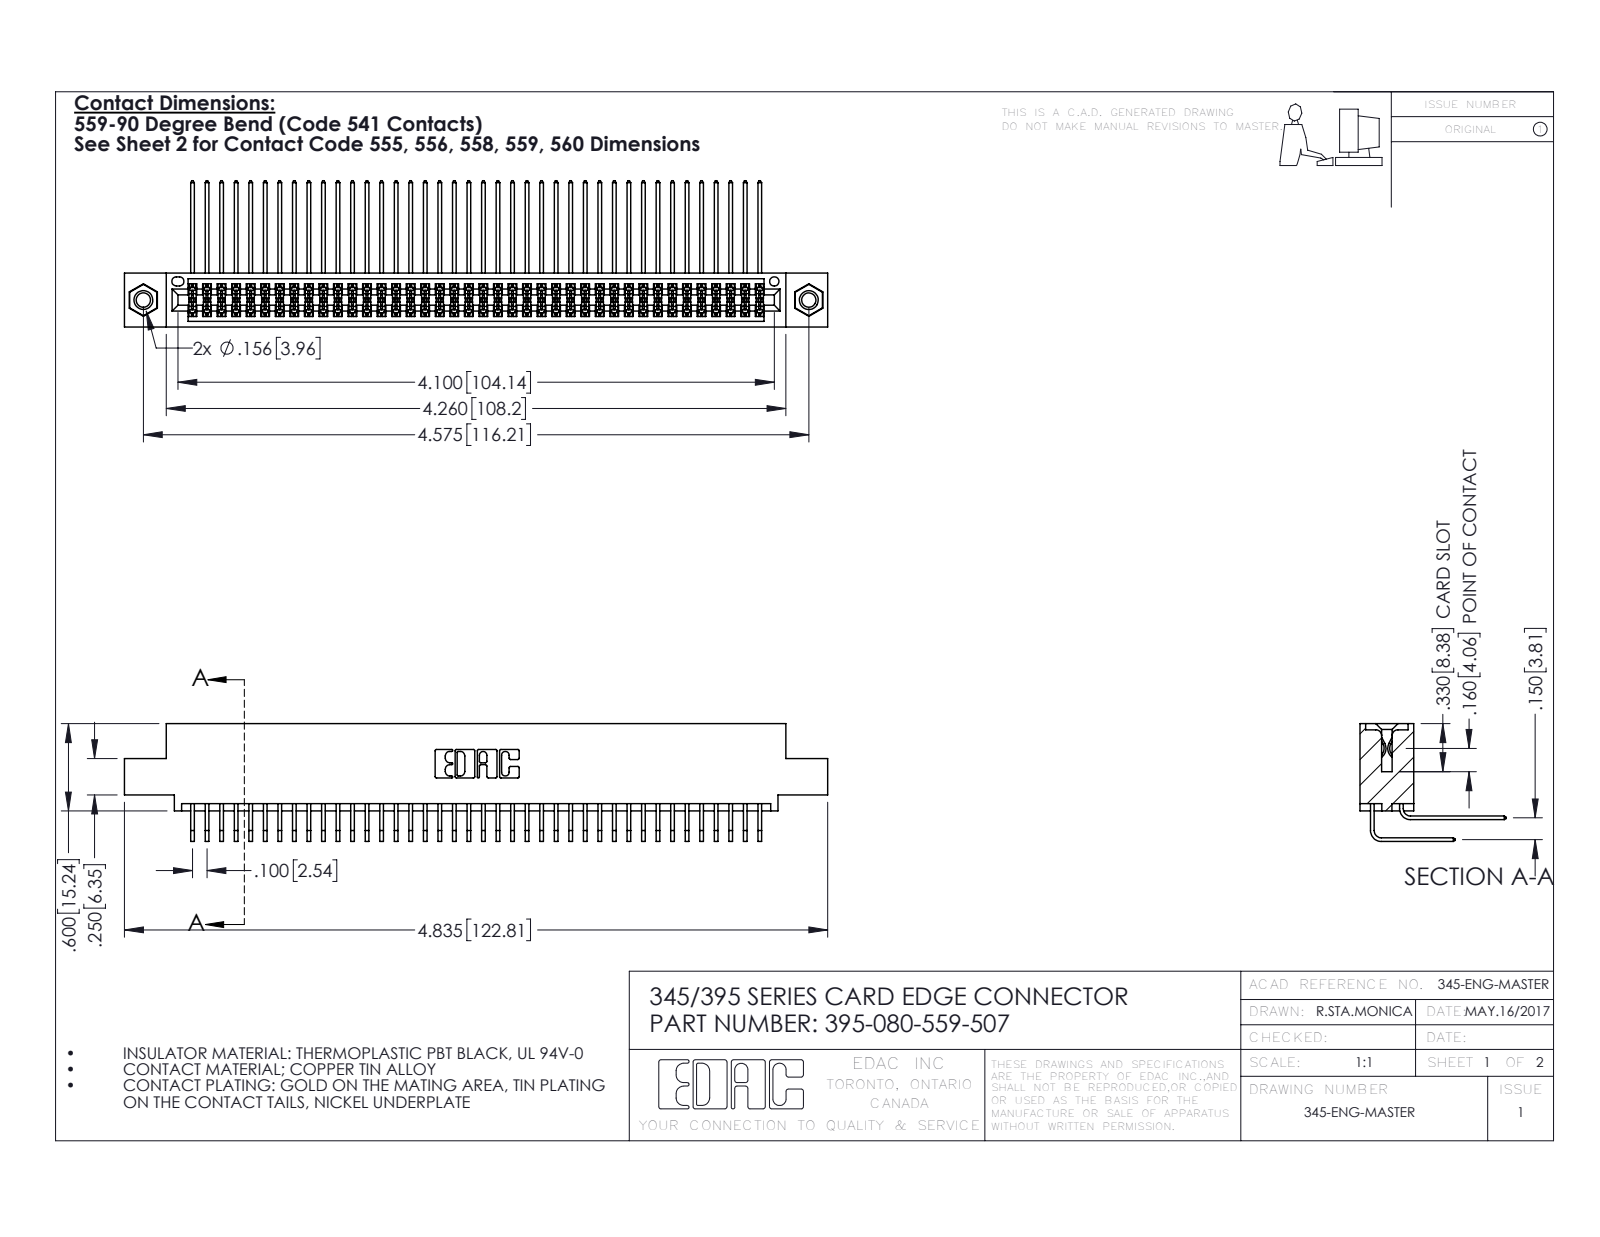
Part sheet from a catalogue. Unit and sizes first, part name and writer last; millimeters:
Units: millimetres
Overall size (bounding box): 122.8 × 25.5 × 20.5
Round holes (diameter × count): ⌀2.5 ×2, ⌀3.2 ×2, ⌀4 ×2, ⌀1.6 ×1
Round bosses / shafts (diameter × count): ⌀3.9 ×2
Partial cylindrical surfaces — rounded edges, fillets, slot ends (radius × count): R0.2 ×120, R0.3 ×22, R0.2 ×6, R0.8 ×6, R0.7 ×3, R0.4 ×2, R0.5 ×2, R0.6 ×2
Main face-to-face distances: 1.8, 7.6, 5.1, 9.4, 2.5, 6.9, 0.6, 5.7, 4.4, 3.8
Hole centre spacings: 6.9, 110.2, 116.2
Volume: 12 300 mm³ · Surface area: 20 410 mm²
Bodies: 83 solids, 4350 faces (2916 planar, 1418 cylindrical, 16 other)
Part name (STEP PRODUCT): 345-292-001_558 559 Tail - 1; 345-292-001_559 Tail - 2; 345 Part_0.110 Offset - 0.156 Dia-TI; 395-080-559-507 (+1 more)
STEP written by: SolidWorks 2016 (CONFIG_CONTROL_DESIGN)
